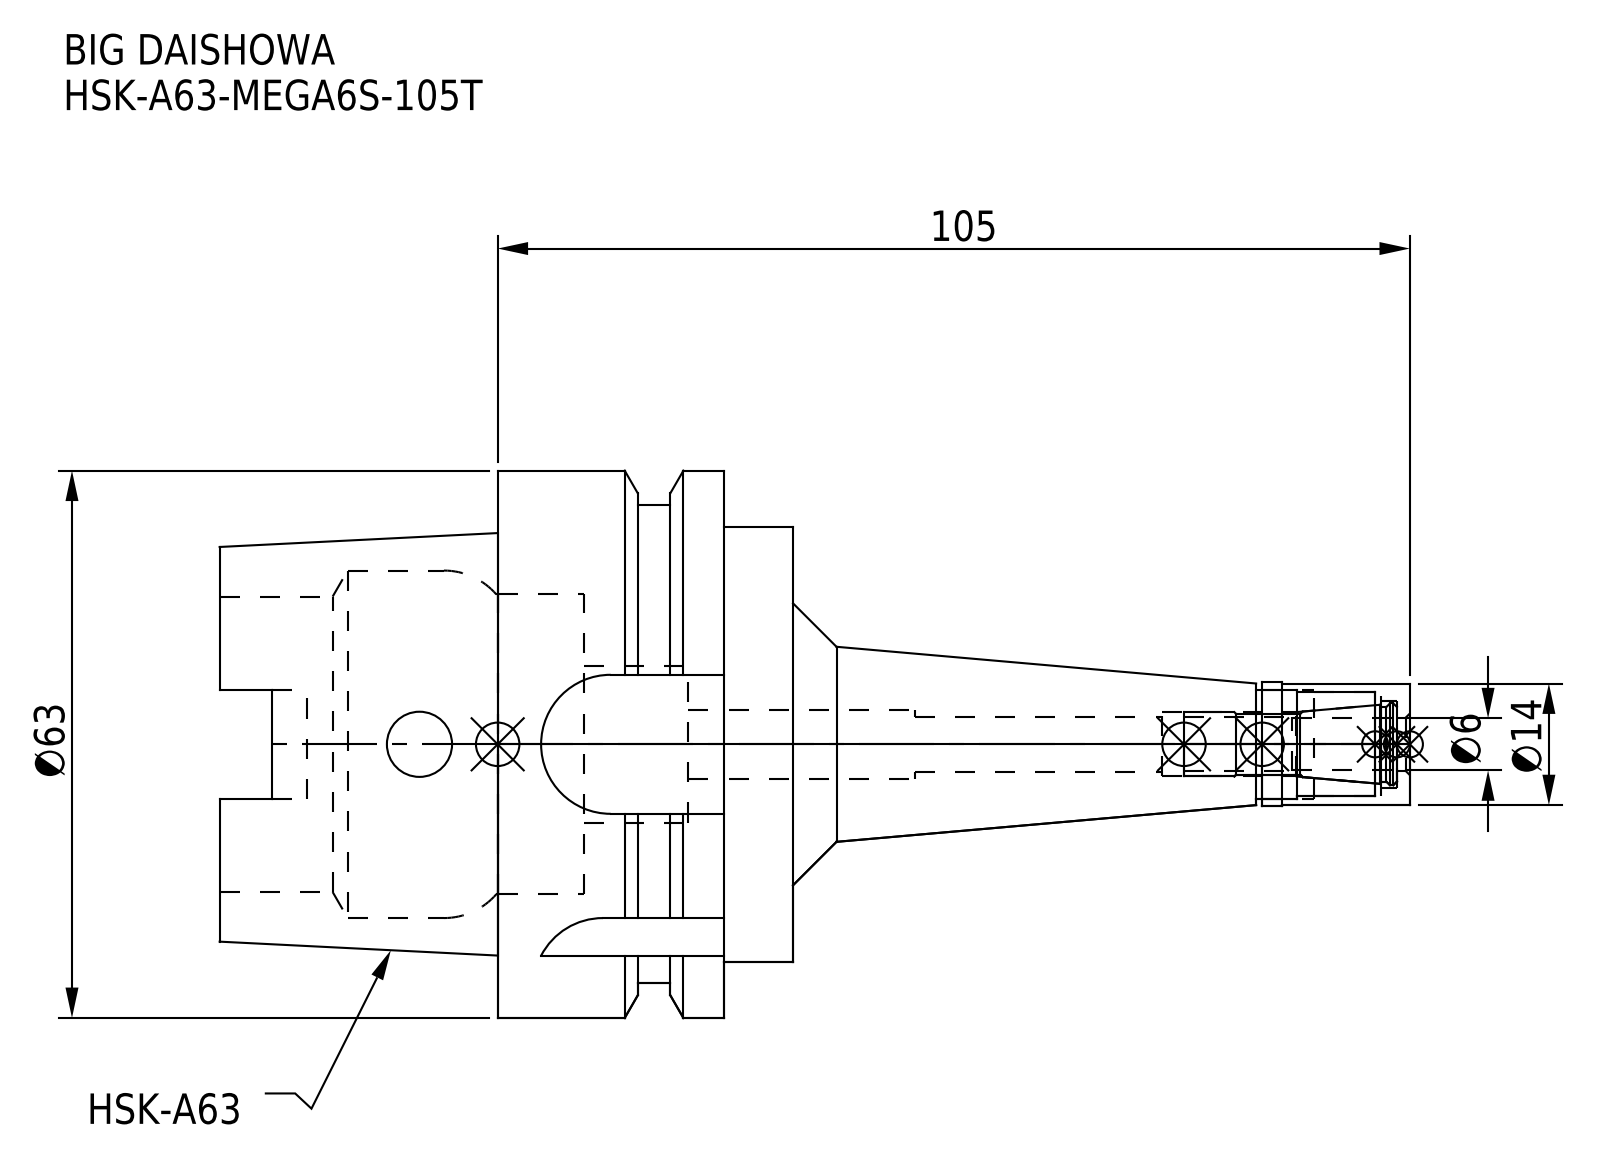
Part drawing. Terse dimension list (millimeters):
name: HSK-A63-MEGA6S-105T; DXF_TEMP_ASSY_ASM_4_ASM.stp; HSK-A63-MEGA6S-105T_1.stp; HSK-A63-MEGA6S-105T-060-FreeParts (+3 more)
written by: SolidWorks 2019 (CONFIG_CONTROL_DESIGN)
unit: mm
bodies: 2 solids, 122 faces (47 planar, 53 cylindrical, 22 other)
size: 137 × 63 × 63
volume: 112 443 mm³; area: 30 167 mm²
holes: 1× ⌀6.1, 1× ⌀6.4, 1× ⌀7.4, 1× ⌀7.5, 1× ⌀8, 1× ⌀10, 1× ⌀12, 1× ⌀12.5, 1× ⌀18, 1× ⌀34, 1× ⌀34.5, 1× ⌀40
bosses: 1× ⌀63, 1× ⌀55, 1× ⌀50, 1× ⌀14.3, 1× ⌀14
rounds: 4× R2.88, 4× R8
face distances: 34, 26, 8, 24.05, 16.05, 9.95, 58, 66, 41.95, 32
